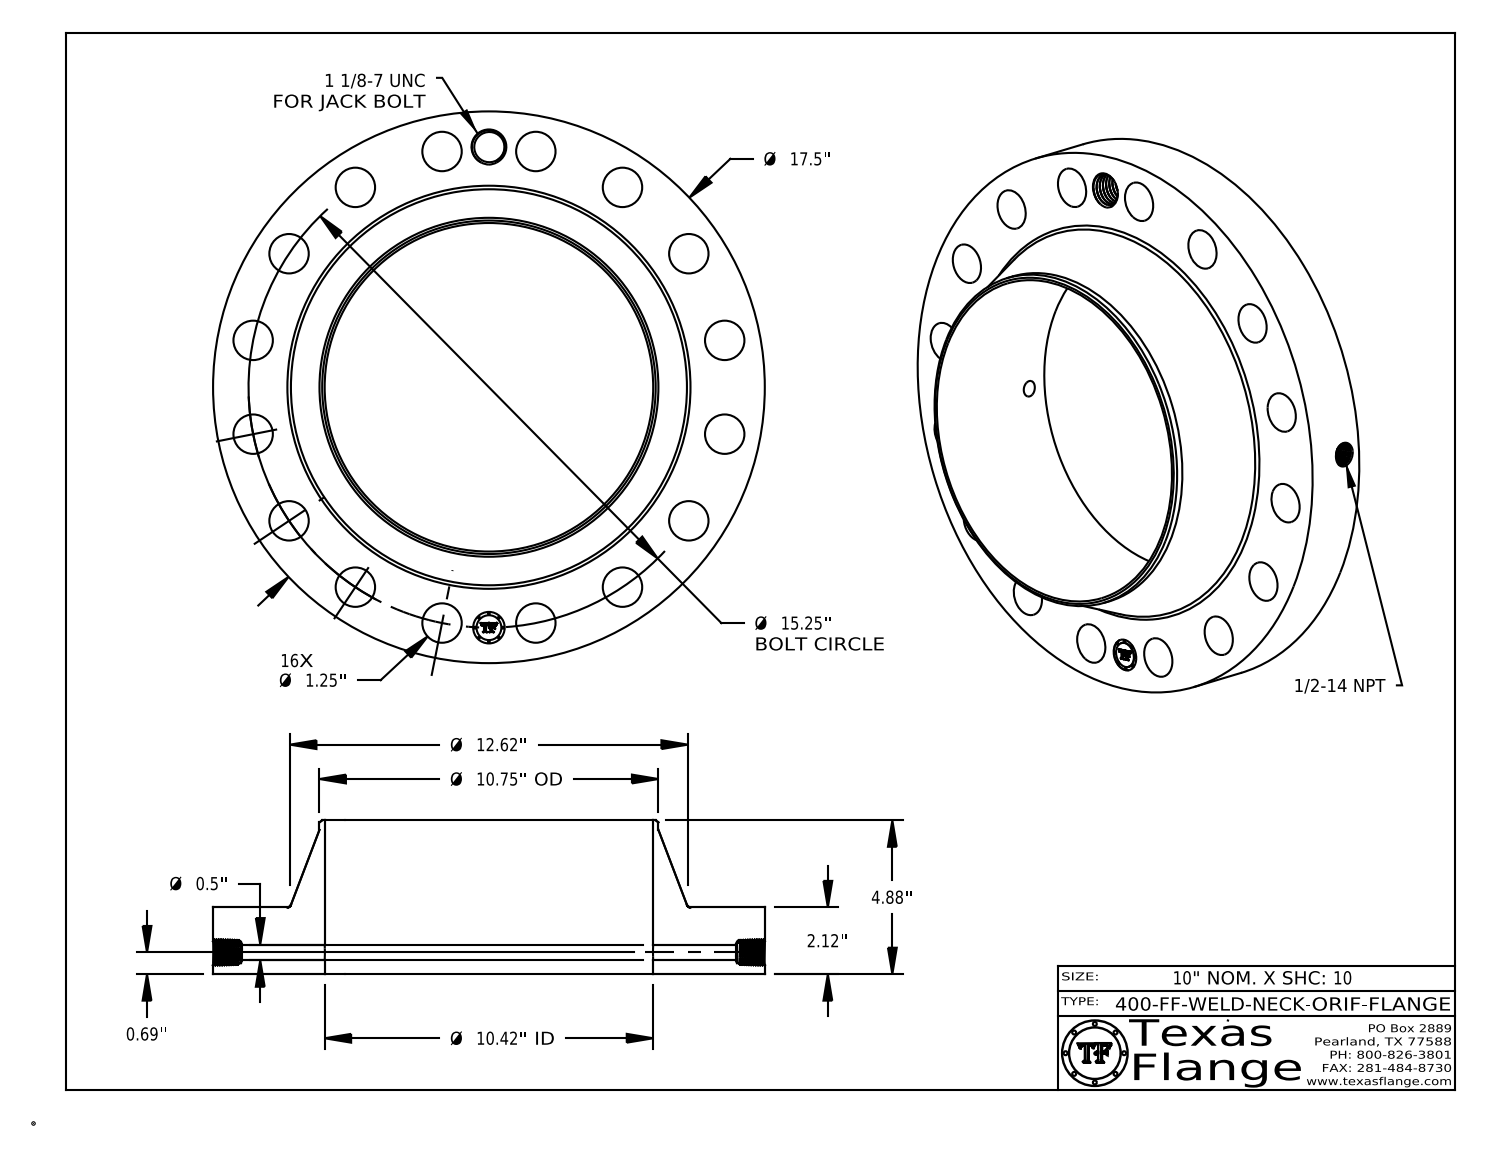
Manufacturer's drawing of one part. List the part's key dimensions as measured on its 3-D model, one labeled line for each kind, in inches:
Part name (STEP PRODUCT): 400-FF-WELD-NECK
STEP written by: CATIA V5 STEP AP214 (AUTOMOTIVE_DESIGN)
Units: inches
Bodies: 1 solid, 782 faces (368 planar, 107 cylindrical, 307 other)
Overall size (bounding box): 17.5 × 17.5 × 4.88
Volume: 340 in³ · Surface area: 773.6 in²
Round holes (diameter × count): ⌀1.25 ×16, ⌀0.5 ×1, ⌀0.672 ×1, ⌀0.984 ×1, ⌀1 ×1, ⌀10.42 ×1
Round bosses / shafts (diameter × count): ⌀0.061 ×8, ⌀17.5 ×1, ⌀10.75 ×1, ⌀0.788 ×1
Main face-to-face distances: 2.12, 4.88, 2.76, 0.015, 2.105, 2.775, 0.298, 0.292, 0.054, 0.248
Hole centre spacings: 5.836, 7.625, 10.783, 14.089, 14.957, 2.975, 2.975, 8.472
